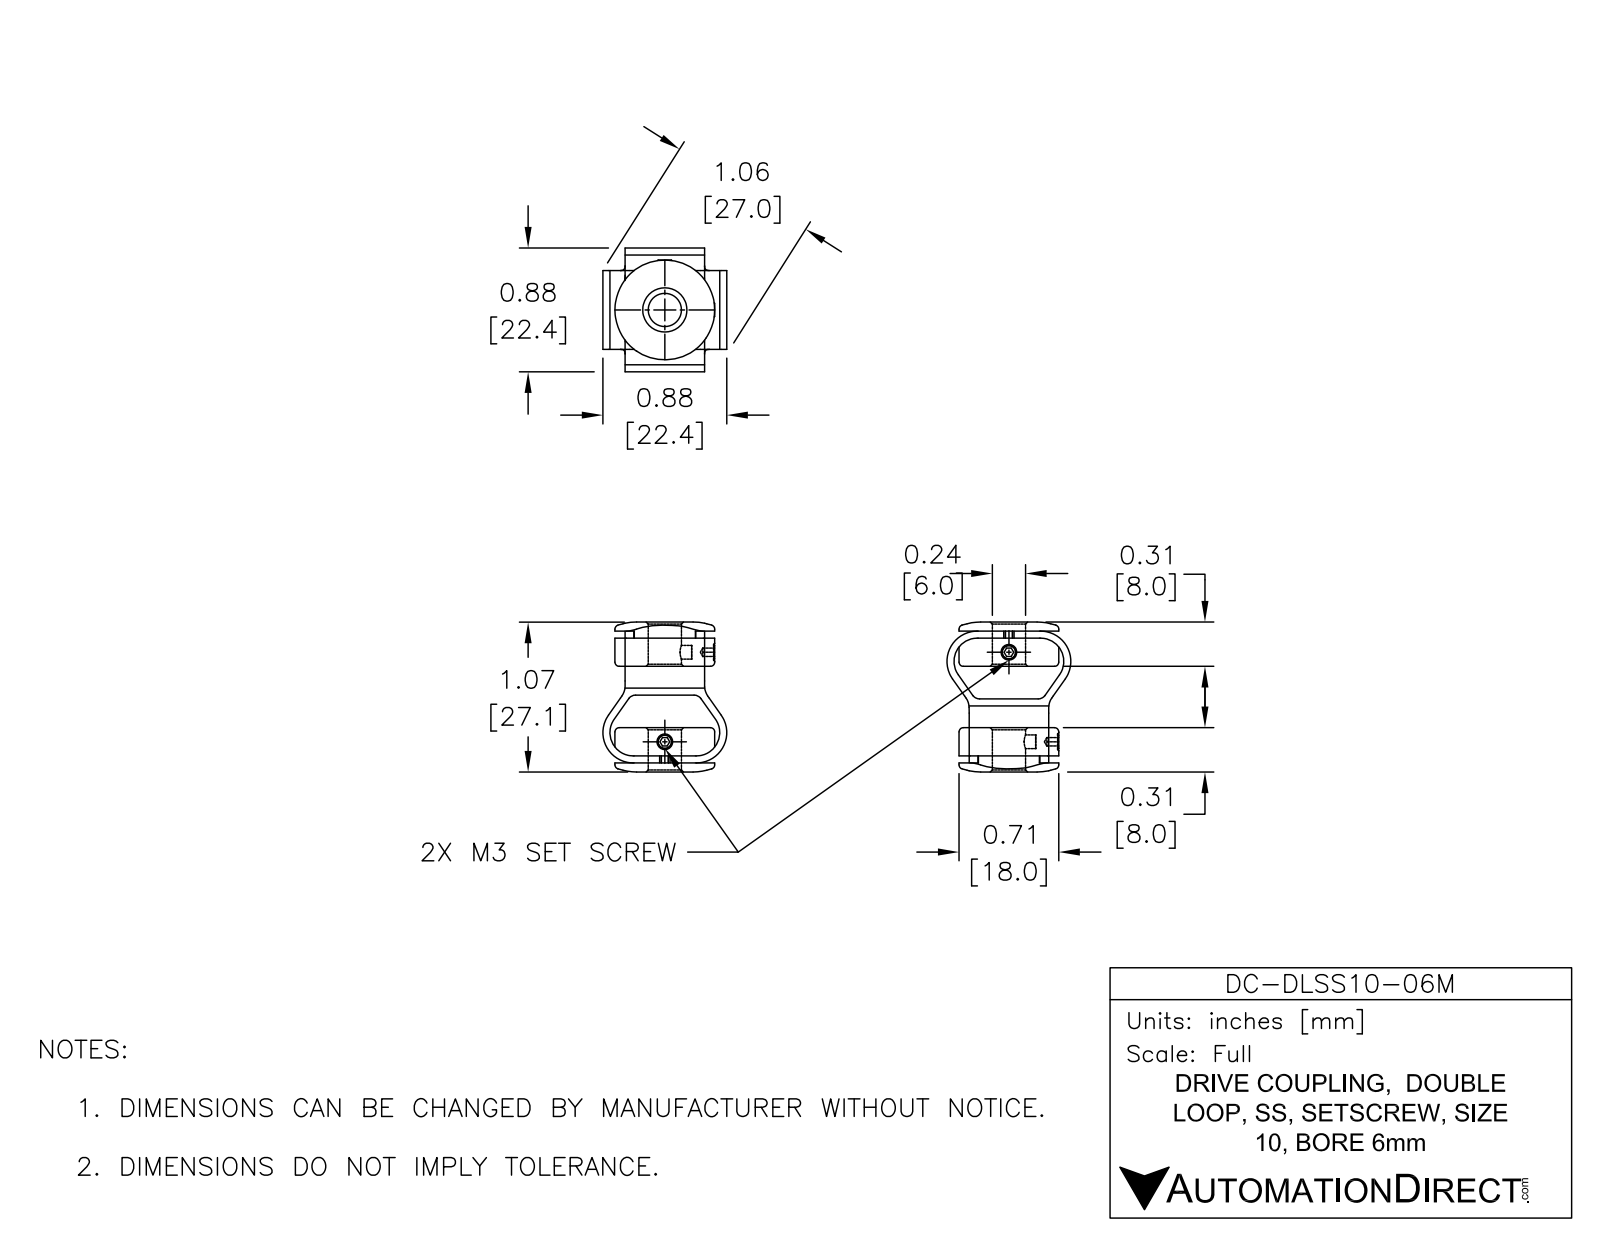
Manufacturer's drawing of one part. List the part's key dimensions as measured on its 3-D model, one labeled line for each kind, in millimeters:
Part name (STEP PRODUCT): DC-DLSS10-06M
STEP written by: SolidWorks 2015 (AUTOMOTIVE_DESIGN)
Units: millimetres
Bodies: 1 solid, 110 faces (57 planar, 28 cylindrical, 25 other)
Overall size (bounding box): 33.4 × 22.35 × 22.35
Volume: 4 193 mm³ · Surface area: 3 959 mm²
Round holes (diameter × count): ⌀6 ×1
Round bosses / shafts (diameter × count): ⌀18.01 ×1
Partial cylindrical surfaces — rounded edges, fillets, slot ends (radius × count): R4.19 ×4, R5.46 ×4, R5.59 ×1
Main face-to-face distances: 1.27, 33.4, 16.38, 17.02, 17.65, 15.75, 7.06, 26.34, 12.23, 11.6
